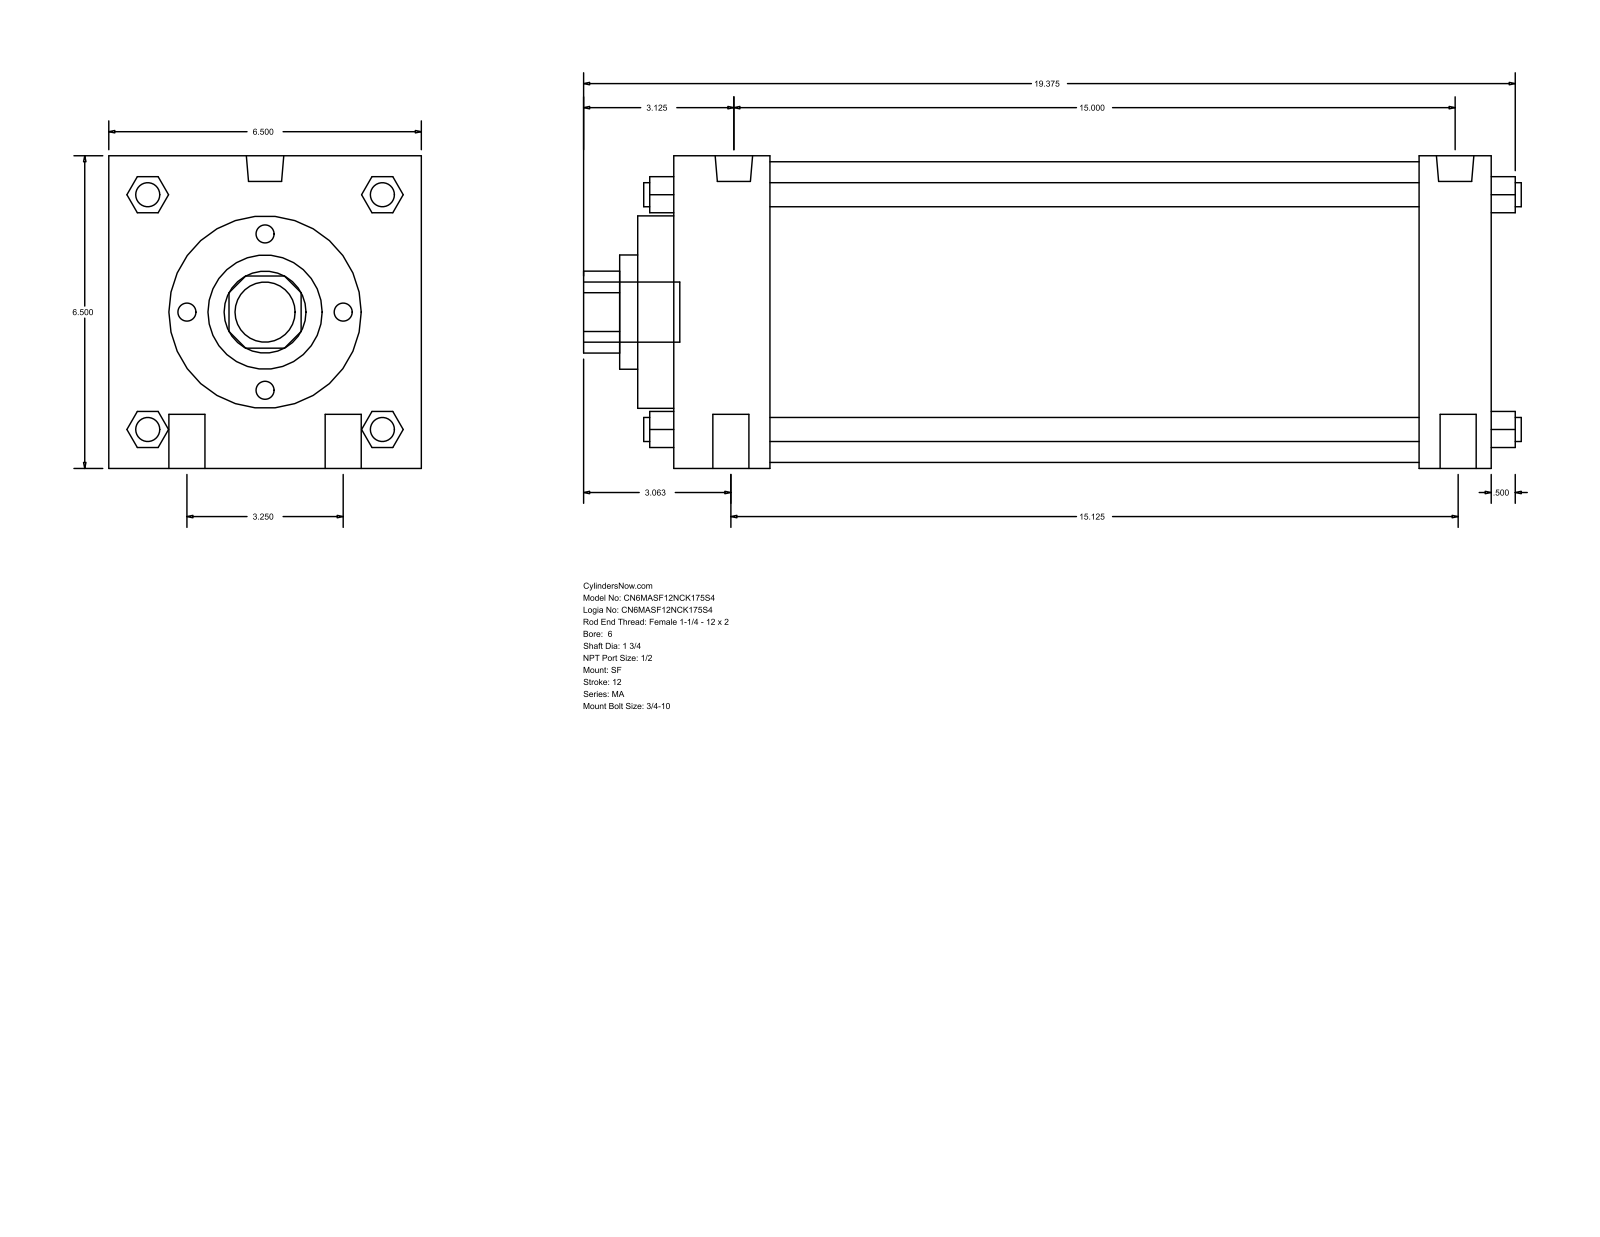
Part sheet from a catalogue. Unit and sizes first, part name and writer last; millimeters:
Units: millimetres
Overall size (bounding box): 495.3 × 165.1 × 165.1
Round holes (diameter × count): ⌀44.45 ×1, ⌀60.33 ×1, ⌀101.6 ×1, ⌀158.75 ×1
Round bosses / shafts (diameter × count): ⌀19.05 ×4, ⌀12.7 ×4, ⌀19.77 ×2, ⌀17.46 ×2, ⌀31.75 ×1
Partial cylindrical surfaces — rounded edges, fillets, slot ends (radius × count): R21.63 ×1
Main face-to-face distances: 165.1, 431.81, 19.05, 50.8, 393.7, 38.11, 342.9, 381.01, 69.85, 412.75
Bodies: 0 solids, 126 faces (95 planar, 31 cylindrical, 0 other)
Part name (STEP PRODUCT): MA_SF__0600_1.75
STEP written by: GSSL Pune (CONFIG_CONTROL_DESIGN)
